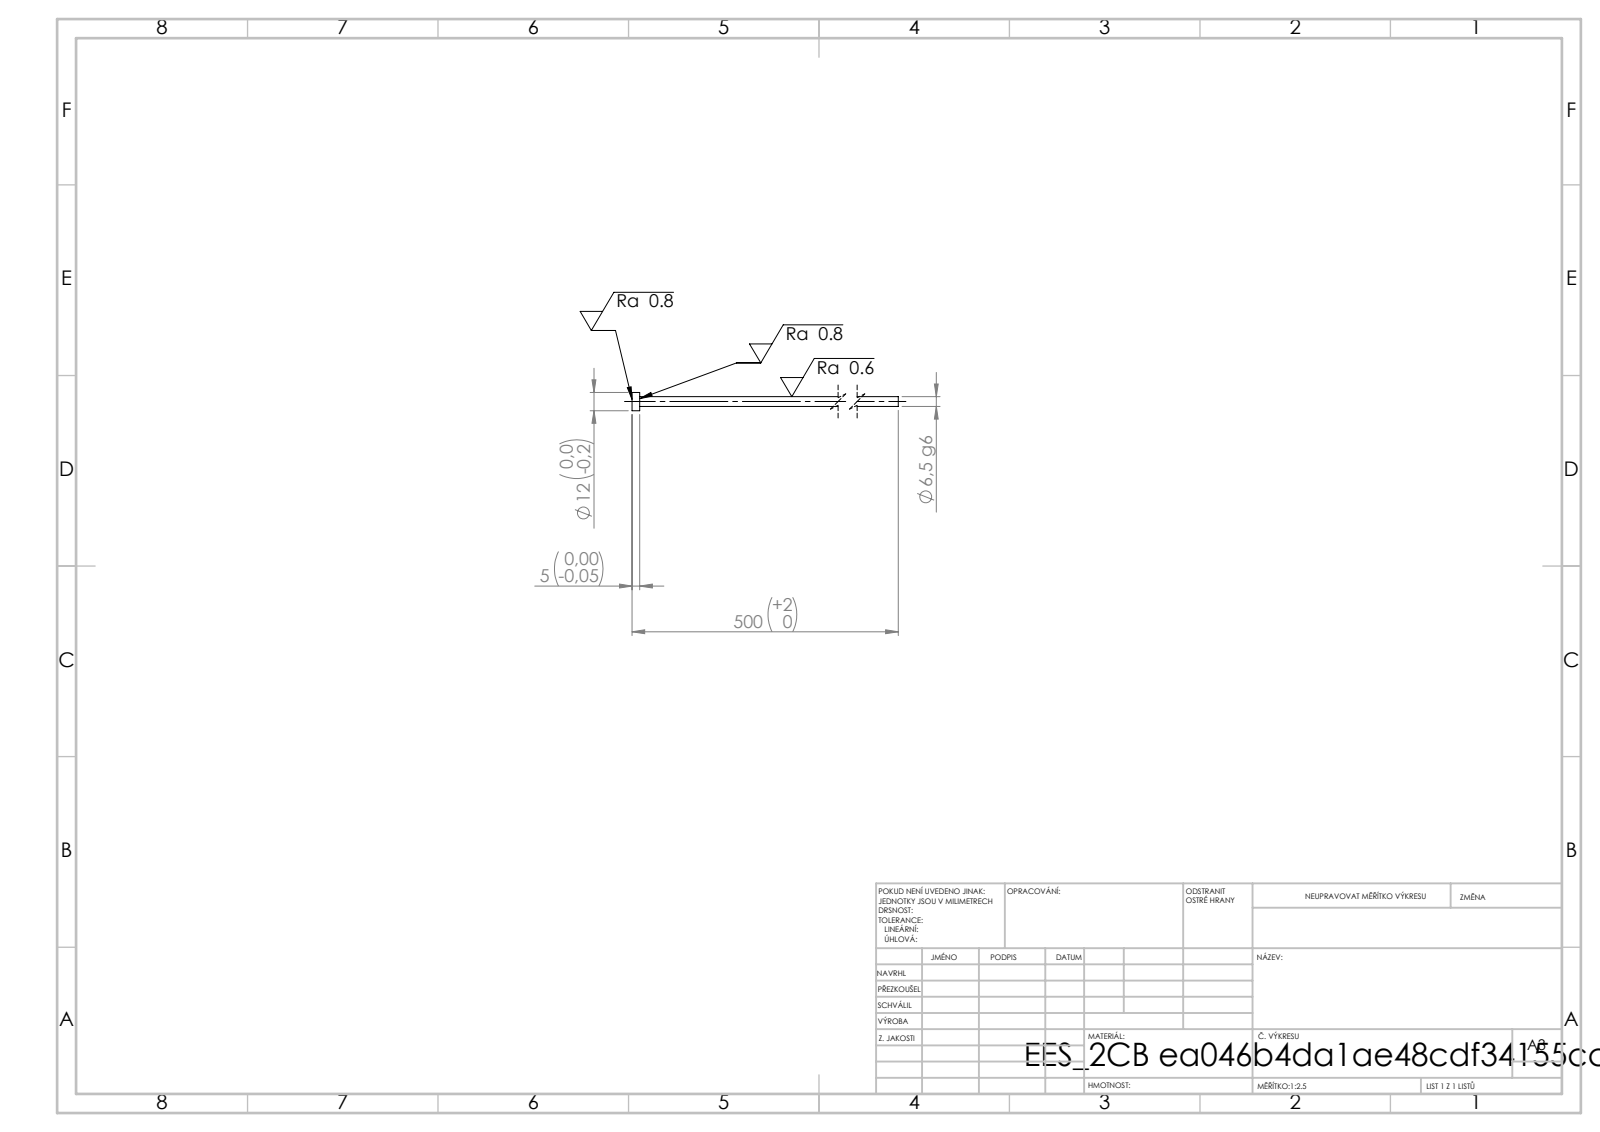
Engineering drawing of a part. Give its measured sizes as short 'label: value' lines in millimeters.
written by: SolidWorks 2019 (CONFIG_CONTROL_DESIGN)
unit: mm
bodies: 1 solid, 7 faces (3 planar, 4 cylindrical, 0 other)
size: 500 × 12 × 12
volume: 16 991 mm³; area: 10 523 mm²
bosses: 1× ⌀12, 1× ⌀6.5
face distances: 5, 500, 495
